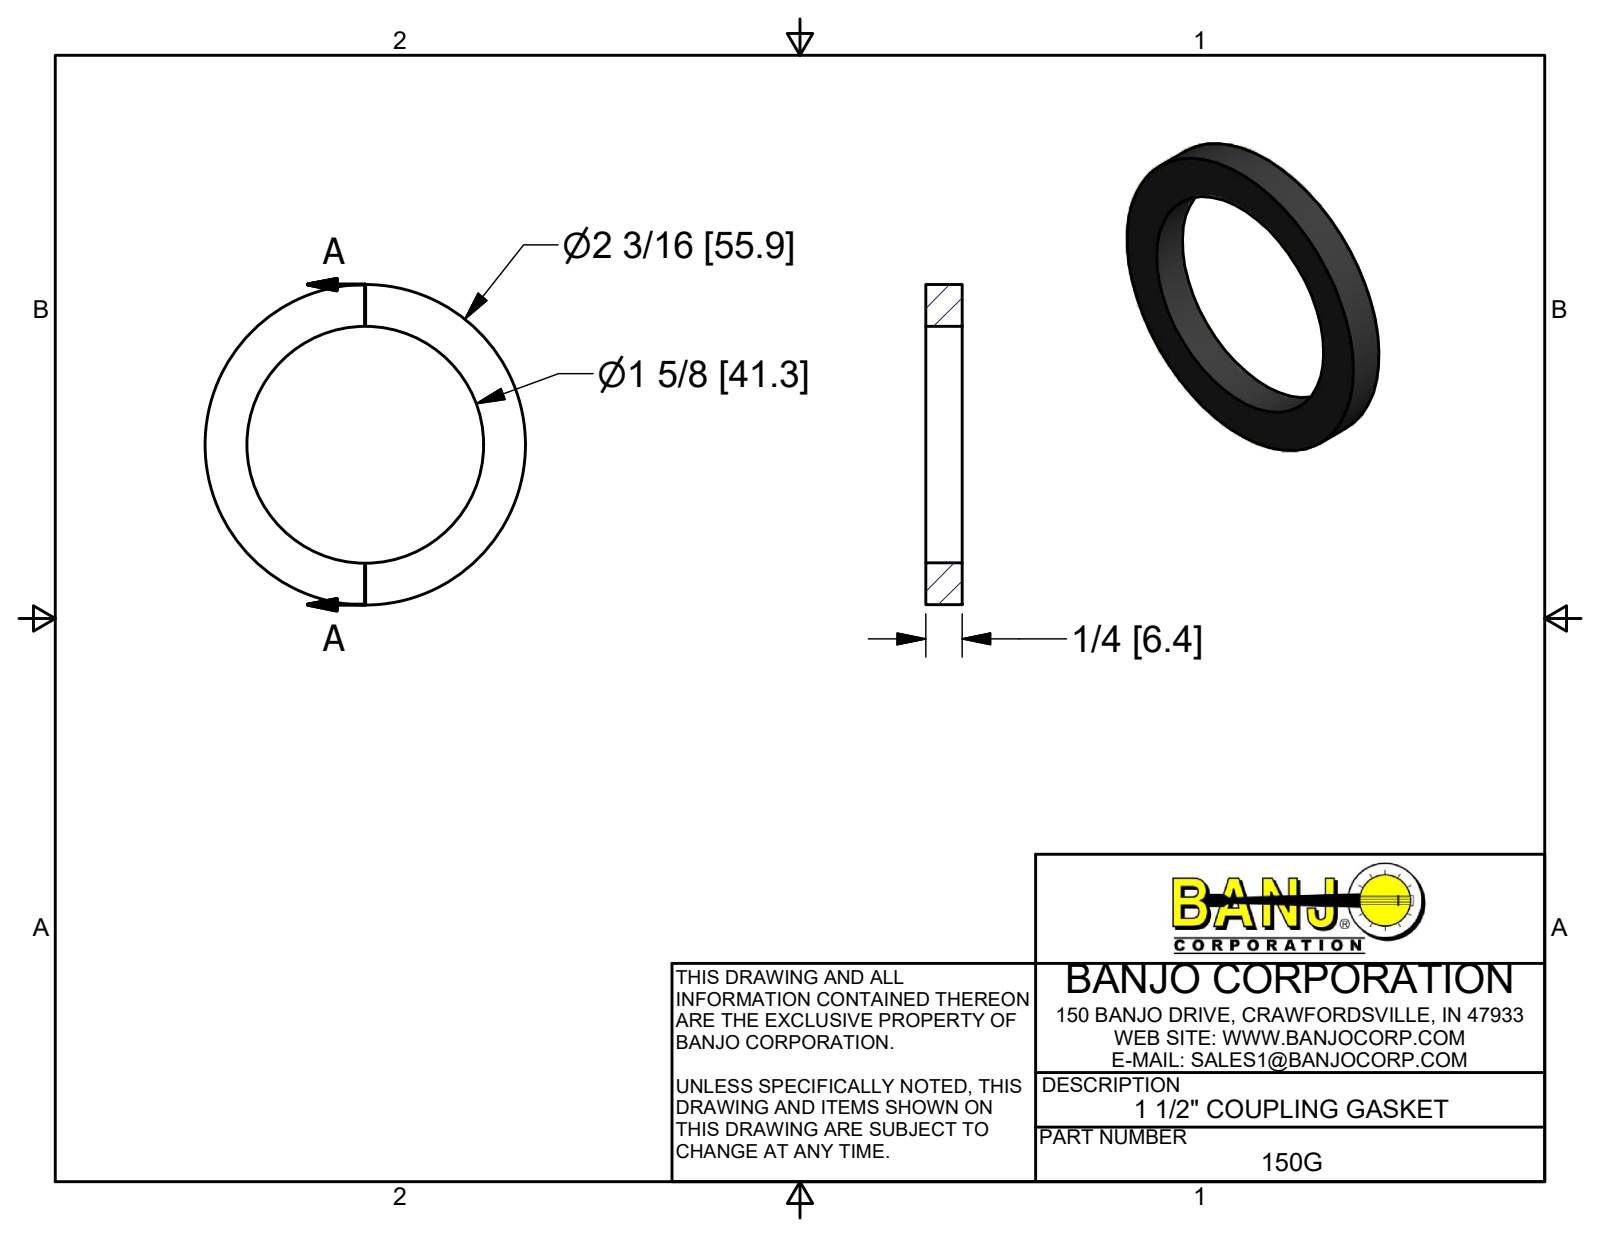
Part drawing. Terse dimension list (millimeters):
name: 150G
written by: Autodesk Inventor 2017 (AUTOMOTIVE_DESIGN)
unit: mm
bodies: 1 solid, 4 faces (2 planar, 2 cylindrical, 0 other)
size: 55.88 × 55.88 × 6.35
volume: 7 077 mm³; area: 4 167 mm²
holes: 1× ⌀41.27
bosses: 1× ⌀55.88
face distances: 6.35
